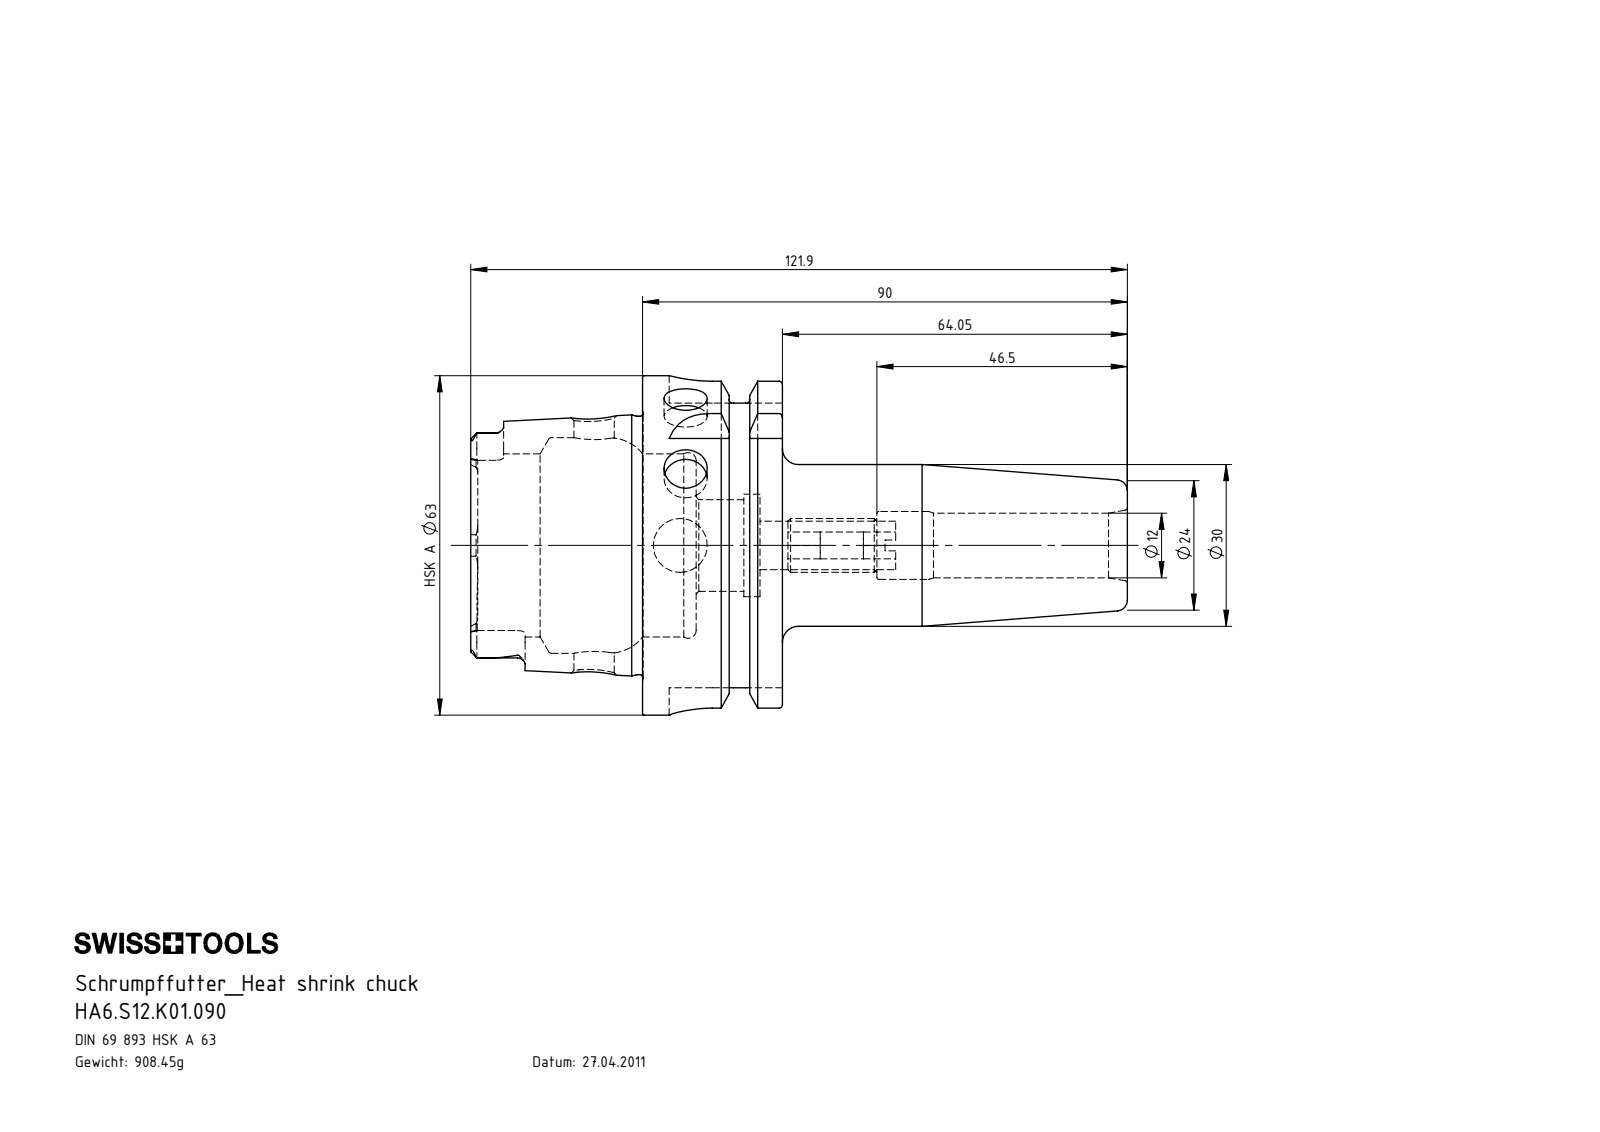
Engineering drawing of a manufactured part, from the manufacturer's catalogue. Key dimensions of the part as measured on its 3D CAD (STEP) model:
Part name (STEP PRODUCT): HA6-S12.K01.090; ERU-AN4.K01.020_A; HA6-S12.K01.090_B_Fertigbearbeitung
STEP written by: SolidWorks 2012 (AUTOMOTIVE_DESIGN)
Units: millimetres
Bodies: 2 solids, 228 faces (82 planar, 59 cylindrical, 87 other)
Overall size (bounding box): 121.9 × 63 × 63
Volume: 115 723 mm³ · Surface area: 30 956 mm²
Round holes (diameter × count): ⌀8 ×2, ⌀5 ×1, ⌀7.5 ×1, ⌀9 ×1, ⌀10 ×1, ⌀12 ×1, ⌀12.6 ×1, ⌀17 ×1, ⌀19 ×1, ⌀34 ×1, ⌀40 ×1
Round bosses / shafts (diameter × count): ⌀63 ×1, ⌀54.95 ×1, ⌀47.94 ×1, ⌀30 ×1, ⌀10 ×1
Partial cylindrical surfaces — rounded edges, fillets, slot ends (radius × count): R1.4 ×6, R2.88 ×4, R8 ×4
Main face-to-face distances: 25.95, 16, 9.95, 31.9, 41.85, 57.85, 52.8, 21.8, 11.85, 53.7
